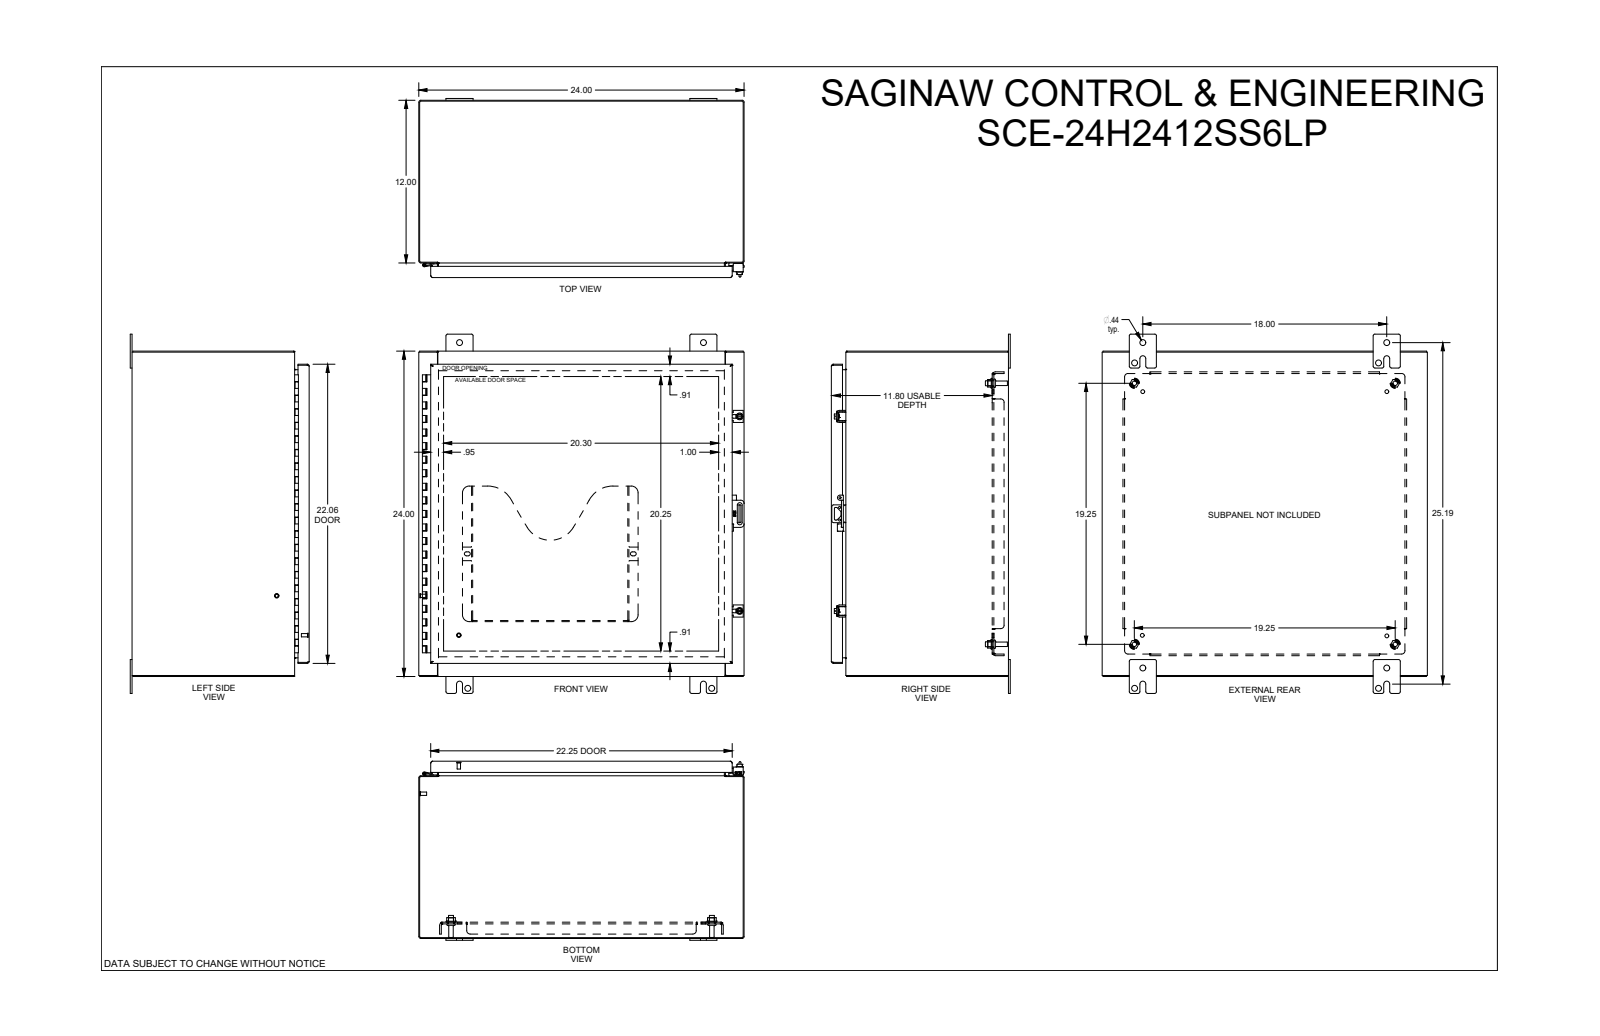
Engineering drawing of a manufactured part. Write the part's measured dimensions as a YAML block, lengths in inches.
part_name: "SCE-24H2412SS6LP"
step_written_by: "SolidWorks 2019 (CONFIG_CONTROL_DESIGN)"
units: inches
bodies: {solids: 0, faces: 3192, planar: 1285, cylindrical: 670, other: 1237}
overall_size: [26.5, 24, 13.208]
round_holes:
  - {diameter: 0.437, count: 8}
  - {diameter: 0.25, count: 5}
  - {diameter: 0.19, count: 4}
  - {diameter: 0.193, count: 4}
  - {diameter: 0.281, count: 4}
  - {diameter: 0.367, count: 4}
  - {diameter: 0.5, count: 4}
  - {diameter: 0.16, count: 2}
  - {diameter: 0.203, count: 2}
  - {diameter: 0.13, count: 1}
  - {diameter: 0.132, count: 1}
round_bosses_or_shafts:
  - {diameter: 0.248, count: 7}
  - {diameter: 0.563, count: 5}
  - {diameter: 0.366, count: 4}
  - {diameter: 0.332, count: 4}
  - {diameter: 0.256, count: 4}
  - {diameter: 0.188, count: 4}
  - {diameter: 0.25, count: 3}
  - {diameter: 0.507, count: 2}
partial_cylinders:
  - {radius: 0.01, count: 114}
  - {radius: 0.015, count: 36}
  - {radius: 0.029, count: 30}
  - {radius: 0.03, count: 27}
  - {radius: 0.125, count: 27}
  - {radius: 0.06, count: 25}
  - {radius: 0.04, count: 22}
  - {radius: 0.07, count: 14}
face_to_face_distances: [0.075, 23.925, 23.85, 24, 12.998, 12.923, 0.075, 1.2, 11.873, 13.073]
hole_center_spacings: [18.641, 0.875, 18, 19.25, 6.5, 26.348, 0.515, 1.439]
